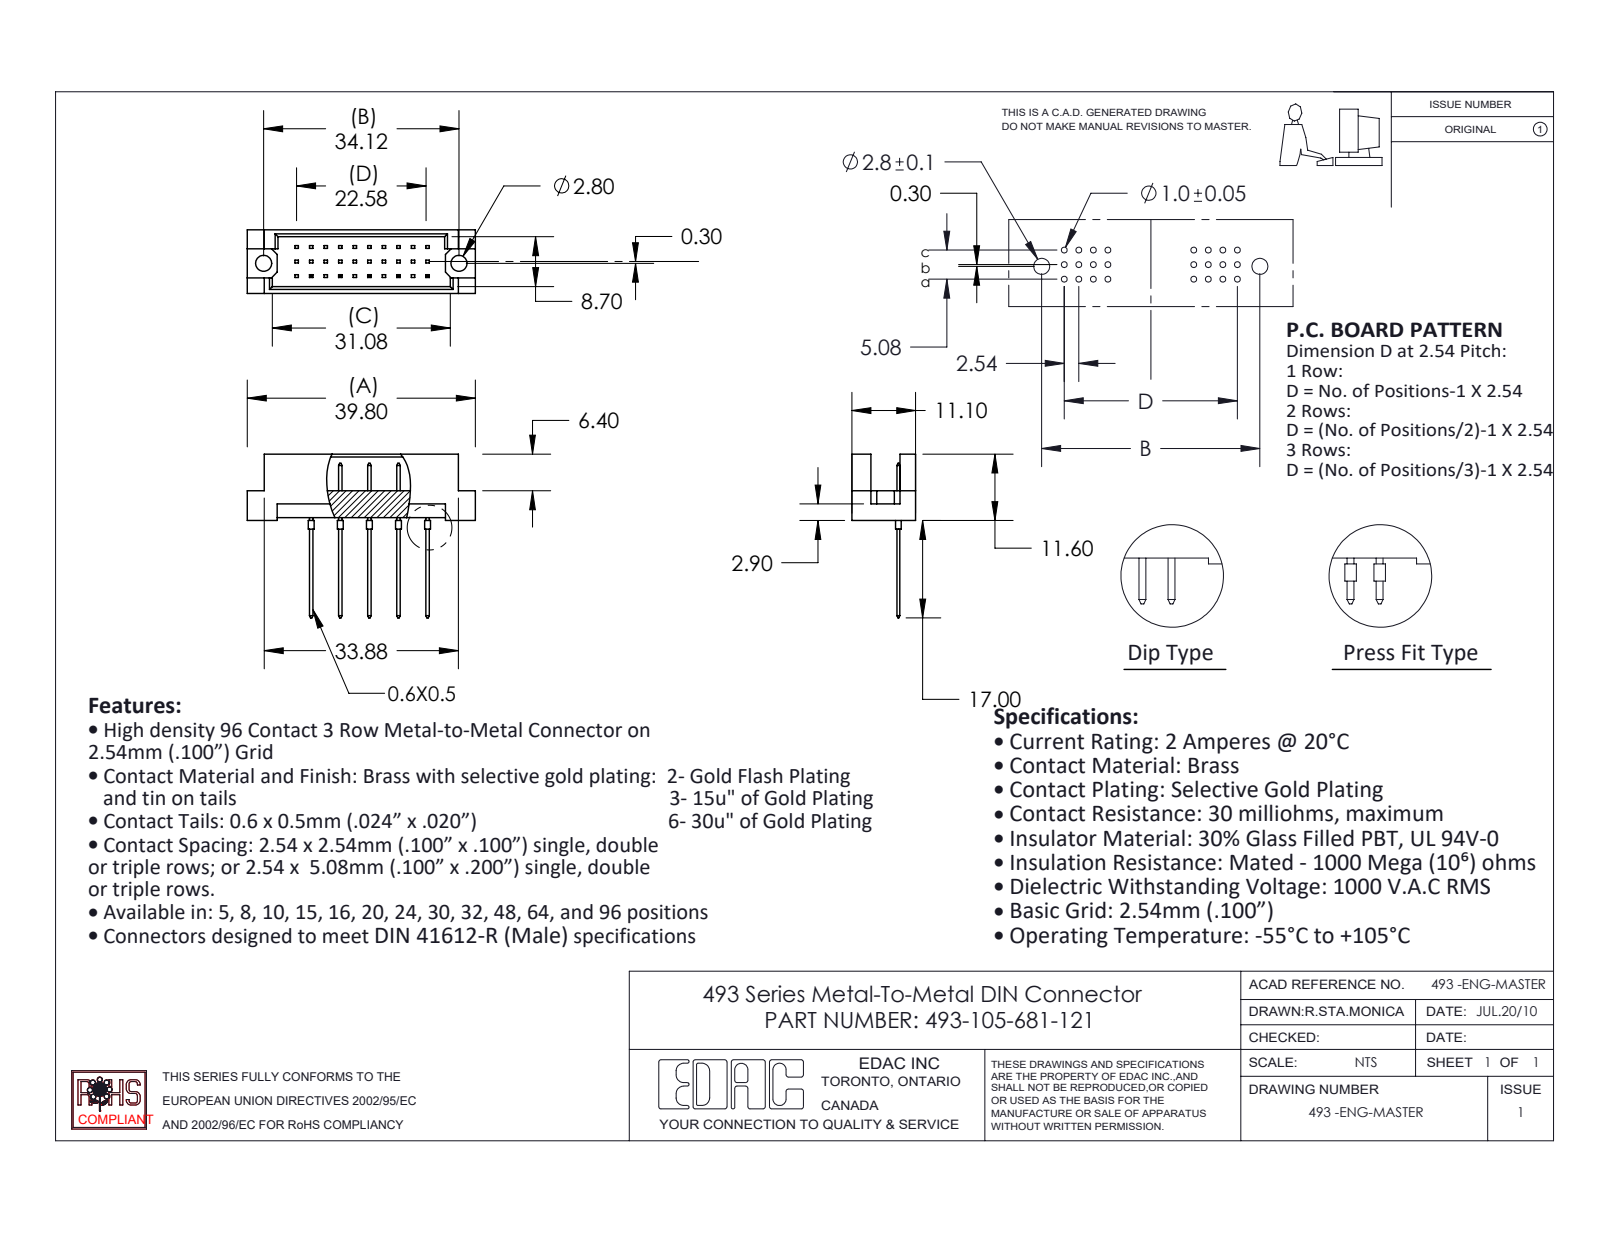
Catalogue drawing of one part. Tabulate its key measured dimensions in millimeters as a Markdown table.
| quantity | value |
| --- | --- |
| part name | 493 Part_30; 493-290_81; 493-105-681-122 |
| STEP written by | SolidWorks 2020 (CONFIG_CONTROL_DESIGN) |
| units | millimeters |
| bodies | 6 solids, 282 faces (268 planar, 14 cylindrical, 0 other) |
| overall size | 39.8 × 28.6 × 11.1 |
| volume | 2 417 mm³ |
| surface area | 3 045 mm² |
| round holes (diameter × count) | 2.8 × 2 |
| round bosses / shafts (diameter × count) | 1 × 5 |
| main face-to-face distances | 1.2, 9.9, 11.1, 8.7, 0.5, 5.08, 4.7, 2.4, 2.76, 8.34 |
| hole center spacings | 34.12 |
